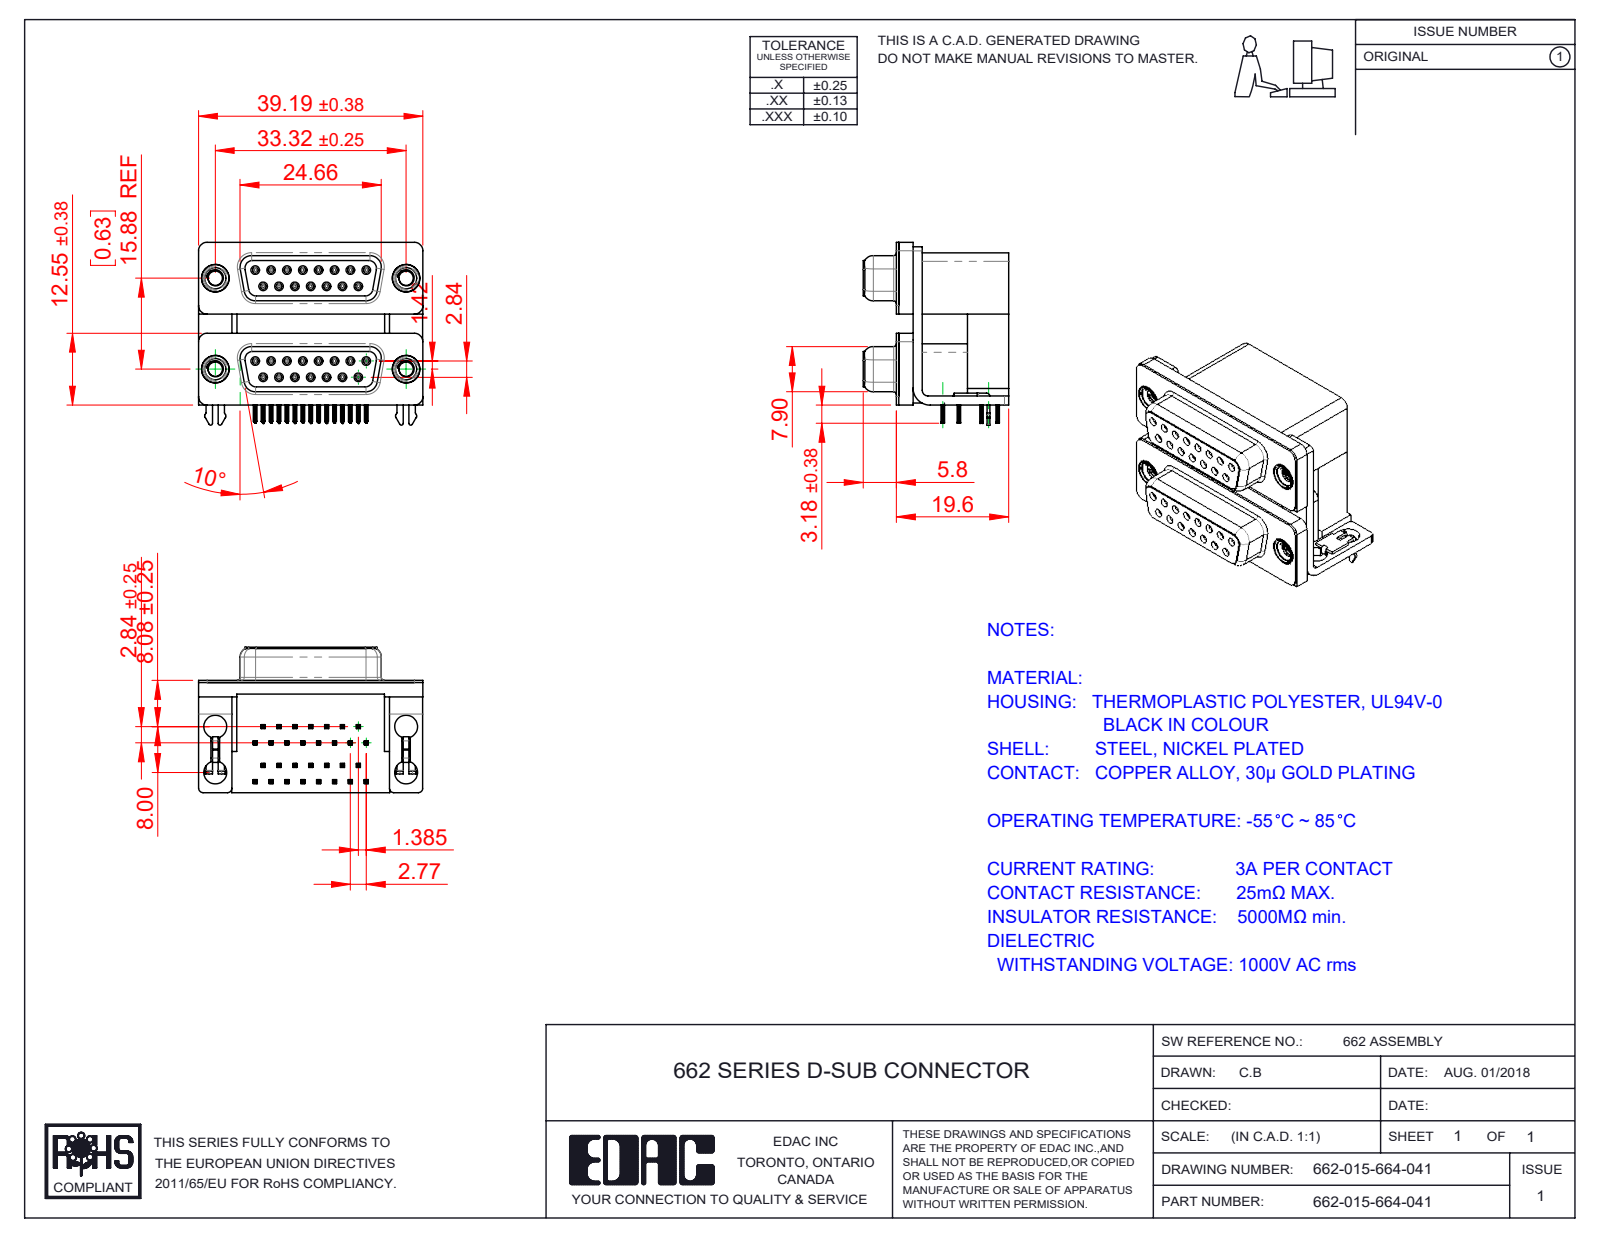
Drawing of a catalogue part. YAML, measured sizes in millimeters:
part_name: "662 Housing Spacer_15 Contacts L; 662 Shell_15 Contacts; 662 Mounting Bracket_2ProngL; 662 Housing Lower_15 Contacts (+8 more)"
step_written_by: "SolidWorks 2020 (CONFIG_CONTROL_DESIGN)"
units: millimeters
bodies: {solids: 43, faces: 4974, planar: 2274, cylindrical: 1212, other: 1488}
overall_size: [39.19, 31.93, 25.4]
volume: 15355
surface_area: 17508
round_holes:
  - {diameter: 0.8, count: 30}
  - {diameter: 0.9, count: 30}
  - {diameter: 4, count: 8}
  - {diameter: 2.5, count: 4}
  - {diameter: 3.5, count: 4}
  - {diameter: 4.8, count: 4}
  - {diameter: 5, count: 4}
round_bosses_or_shafts:
  - {diameter: 1.2, count: 30}
  - {diameter: 4.9, count: 4}
  - {diameter: 4.75, count: 4}
  - {diameter: 3.9, count: 4}
partial_cylinders:
  - {radius: 0.1, count: 241}
  - {radius: 0.15, count: 120}
  - {radius: 0.35, count: 60}
  - {radius: 0.34, count: 30}
  - {radius: 1.35, count: 16}
  - {radius: 1.5, count: 15}
  - {radius: 0.28, count: 14}
  - {radius: 0.5, count: 12}
face_to_face_distances: [0.4, 19.2, 16.7, 2.5, 10.7, 2.9, 7.2, 9.5, 12, 15.88]
hole_center_spacings: [3.16, 16.12, 2.77, 16.82, 5.54, 8.31, 15.88, 17.92]
